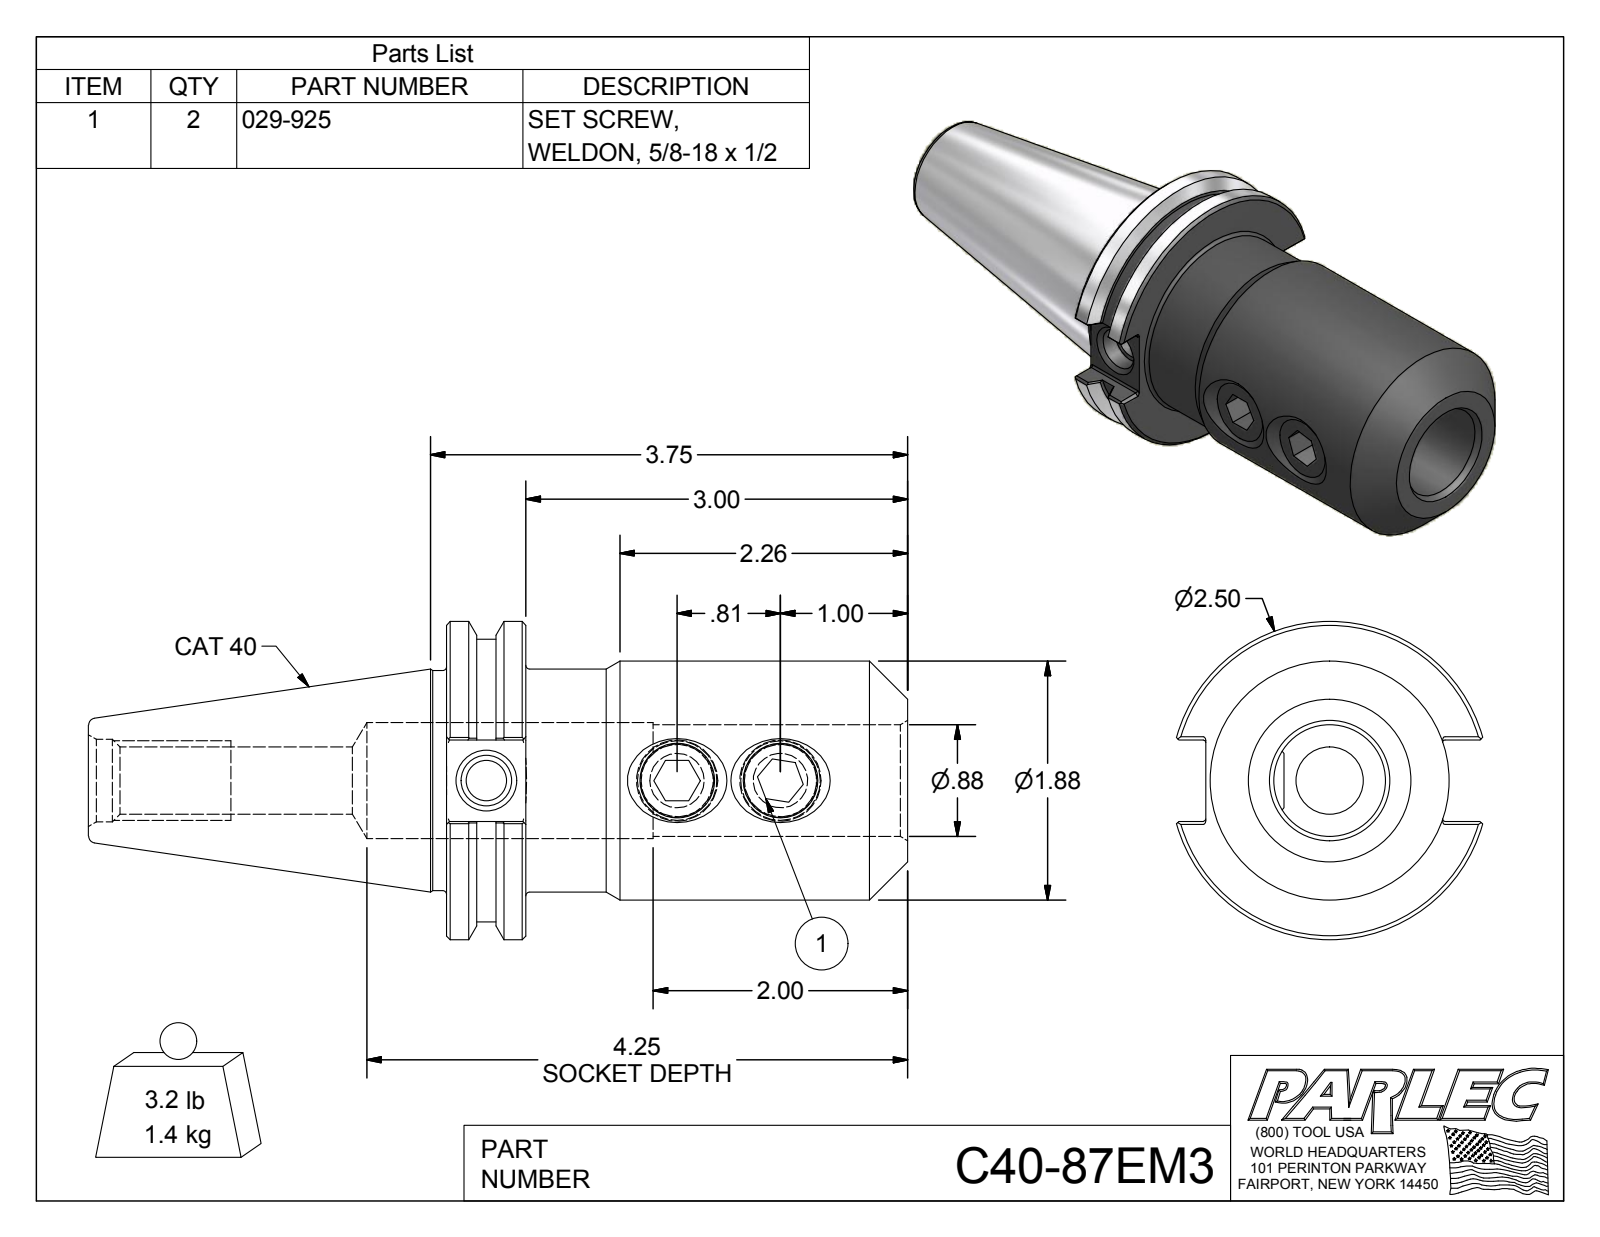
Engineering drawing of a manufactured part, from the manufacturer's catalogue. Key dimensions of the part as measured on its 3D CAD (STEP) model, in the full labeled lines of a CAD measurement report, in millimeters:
Part name (STEP PRODUCT): C40-87EM3; C40-87EM3-1; 029-925
STEP written by: Autodesk Inventor 2012 (AUTOMOTIVE_DESIGN)
Units: millimetres
Bodies: 3 solids, 121 faces (51 planar, 33 cylindrical, 37 other)
Overall size (bounding box): 163.5 × 63.5 × 61.1
Volume: 186 000 mm³ · Surface area: 40 460 mm²
Round holes (diameter × count): ⌀14.7 ×2, ⌀8 ×1, ⌀10.1 ×1, ⌀13.4 ×1, ⌀16.5 ×1, ⌀22.2 ×1, ⌀23.1 ×1
Round bosses / shafts (diameter × count): ⌀15.9 ×2, ⌀63.5 ×1, ⌀56.4 ×1, ⌀47.6 ×1, ⌀44.5 ×1, ⌀43.9 ×1
Partial cylindrical surfaces — rounded edges, fillets, slot ends (radius × count): R0.5 ×12
Main face-to-face distances: 15.9, 92.1, 76.2, 8, 44.3, 31.6, 12.7, 16.3, 47.2, 15.6
Hole centre spacings: 20.6, 38, 58.7
